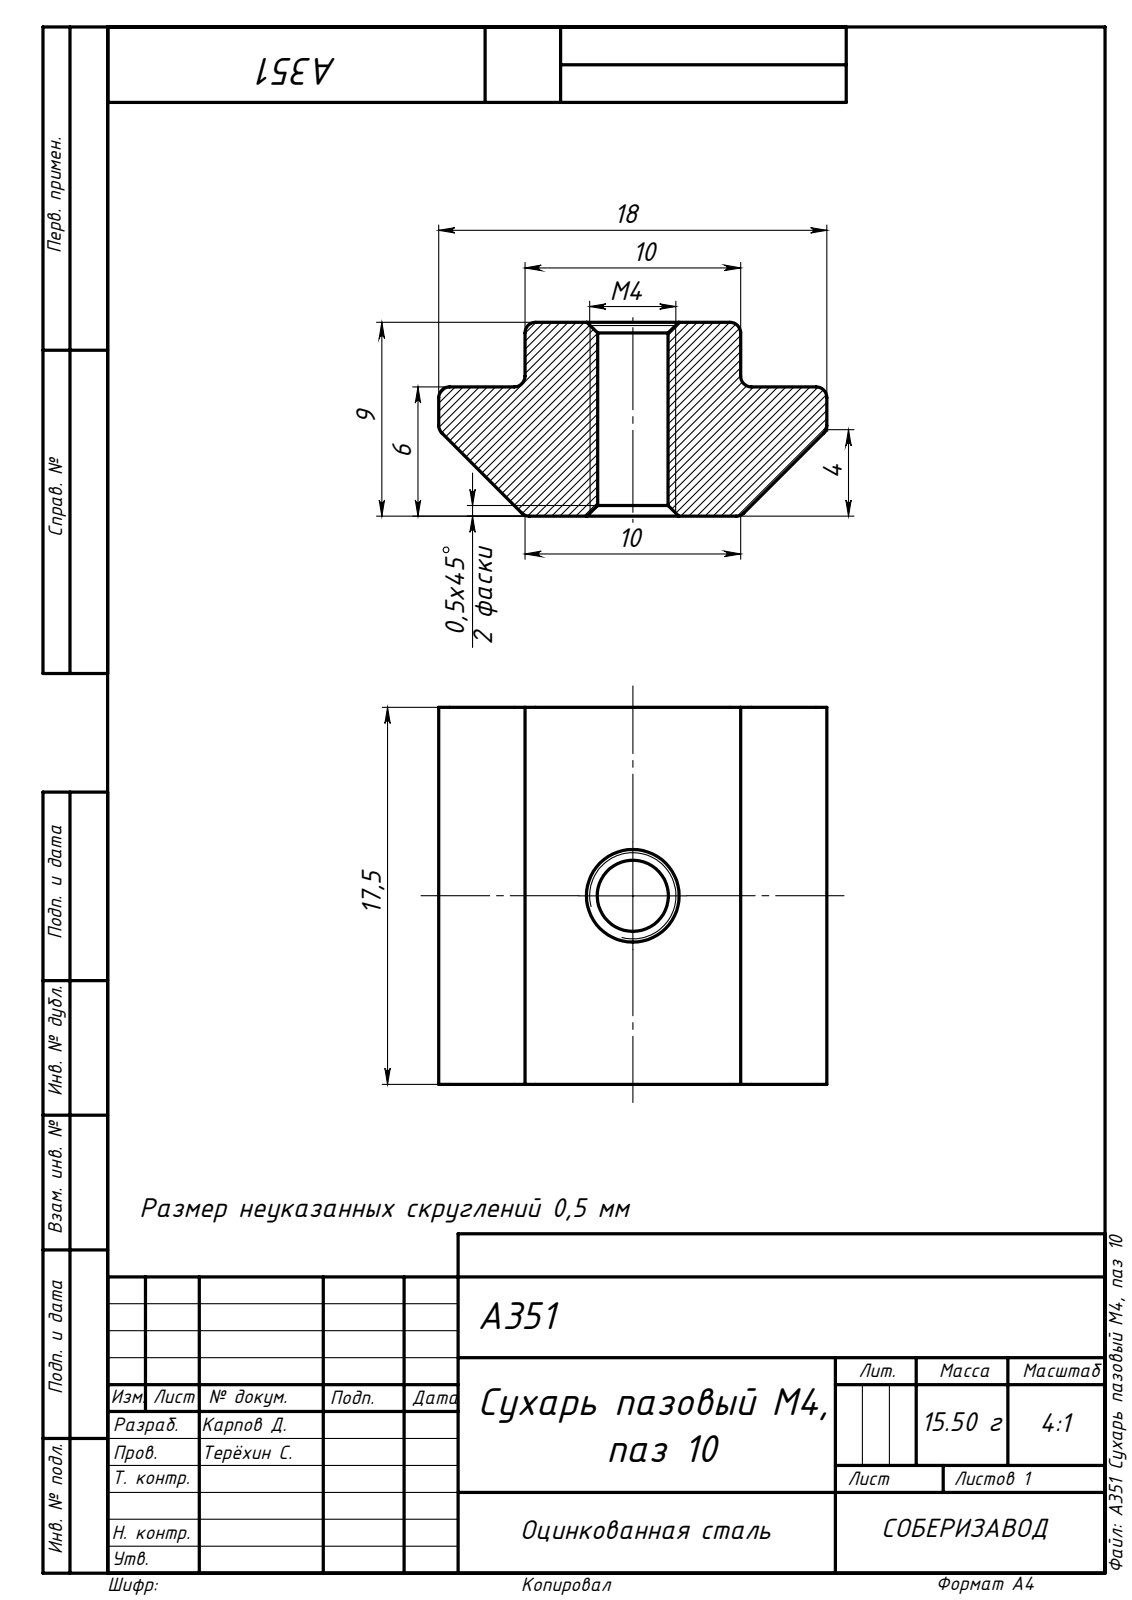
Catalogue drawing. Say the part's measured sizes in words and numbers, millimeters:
The part is named "A351 Сухарь пазовый M4, паз 10". Its 3-D file was written by "SolidWorks 2018 (AUTOMOTIVE_DESIGN)". It is 1 solid with 28 faces: 12 planar, 12 cylindrical and 4 other. Overall it measures 18 by 17.5 by 9 millimeters. Its volume is 2 053 cubic millimeters and its surface area 1 153 square millimeters. Round holes: 1 of diameter 3.3. Partial cylindrical surfaces (rounded edges, fillets, slot ends): 10 of radius 0.5. The main face-to-face distances are 9, 17.5, 3, 6, 4, 14, 10, 18.
